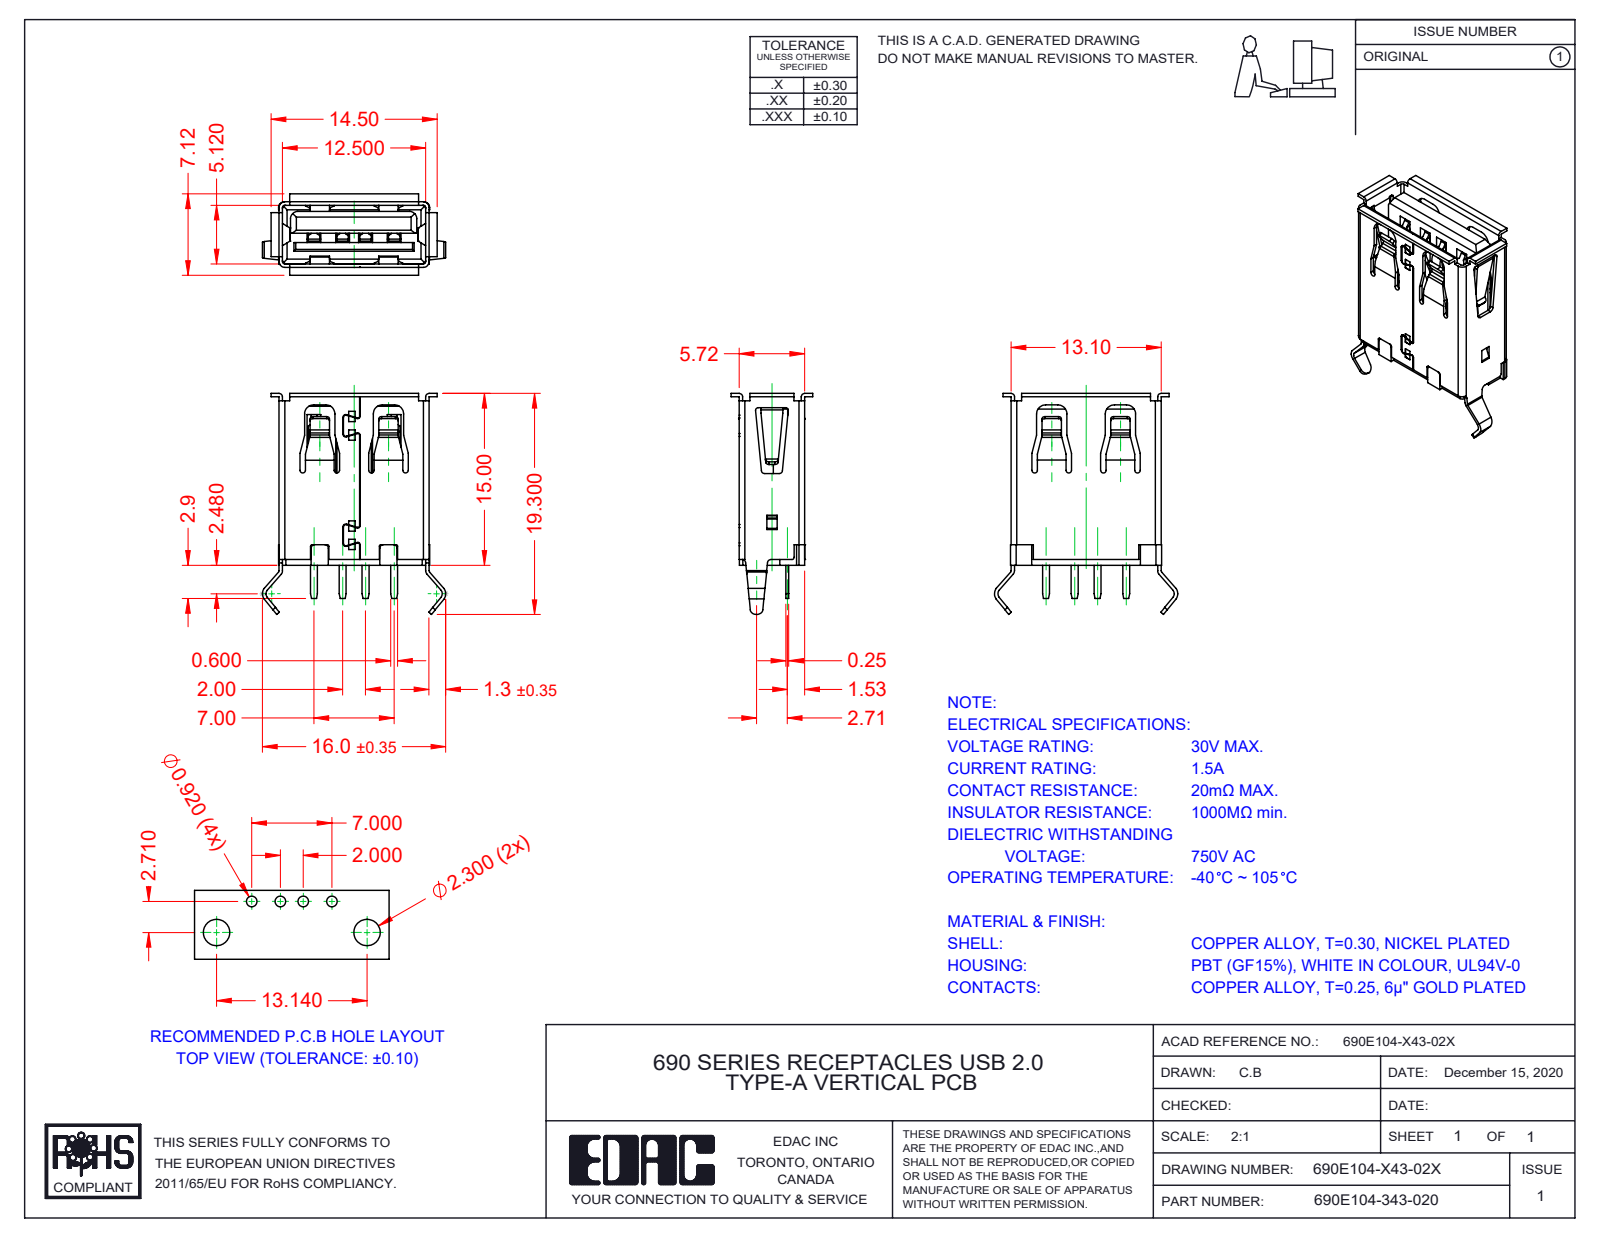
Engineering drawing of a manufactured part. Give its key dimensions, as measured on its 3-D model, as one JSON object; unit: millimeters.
{"part_name": "Contact 690E104-X43-02X; 690E104-243-020; Insulator2 690E104-X43-02X_White; Insulator1 690E104-X43-02X_White (+1 more)", "step_written_by": "SolidWorks 2020 (AUTOMOTIVE_DESIGN)", "units": "millimeters", "bodies": {"solids": 7, "faces": 825, "planar": 618, "cylindrical": 207, "other": 0}, "overall_size": [19.3, 16, 7.12], "volume_mm3": 620, "surface_area_mm2": 2264, "partial_cylinders_radius": [[0.2, 37], [0.3, 26], [0.15, 25], [0.5, 15], [0.25, 13], [0.8, 6], [0.56, 4], [0.62, 4]], "face_to_face_distances": [5.42, 5.12, 5.72, 2.5, 1.09, 12.8, 1.2, 4.5, 1.39, 4.03]}
